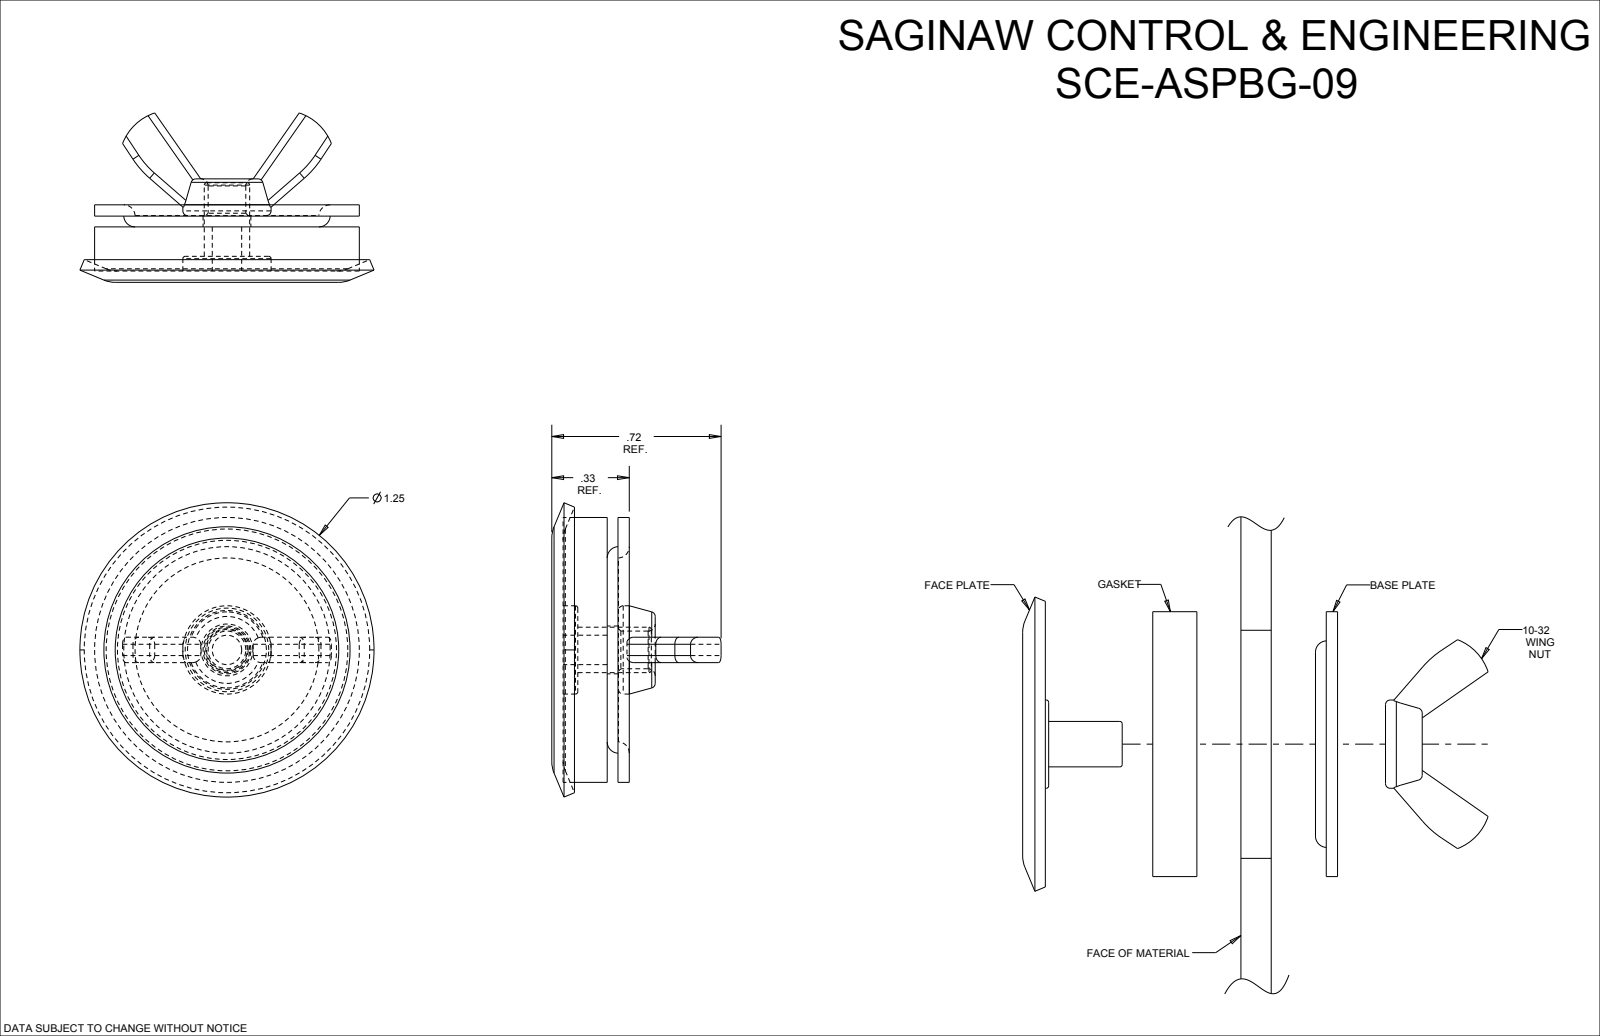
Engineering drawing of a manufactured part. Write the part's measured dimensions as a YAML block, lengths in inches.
part_name: "SCE-ASPB-05"
step_written_by: "SolidWorks 2019 (AUTOMOTIVE_DESIGN)"
units: inches
bodies: {solids: 5, faces: 79, planar: 28, cylindrical: 24, other: 27}
overall_size: [1.25, 1.25, 0.754]
volume: 0.328
surface_area: 8.823
round_holes:
  - {diameter: 0.19, count: 1}
  - {diameter: 0.203, count: 1}
round_bosses_or_shafts:
  - {diameter: 1.125, count: 1}
  - {diameter: 0.375, count: 1}
  - {diameter: 0.188, count: 1}
partial_cylinders:
  - {radius: 0.03, count: 12}
  - {radius: 0.22, count: 2}
  - {radius: 0.4, count: 2}
face_to_face_distances: [0.048, 0.187, 0.27, 0.046, 0.315, 0.235, 0.082, 0.318, 0.034, 0.222]
